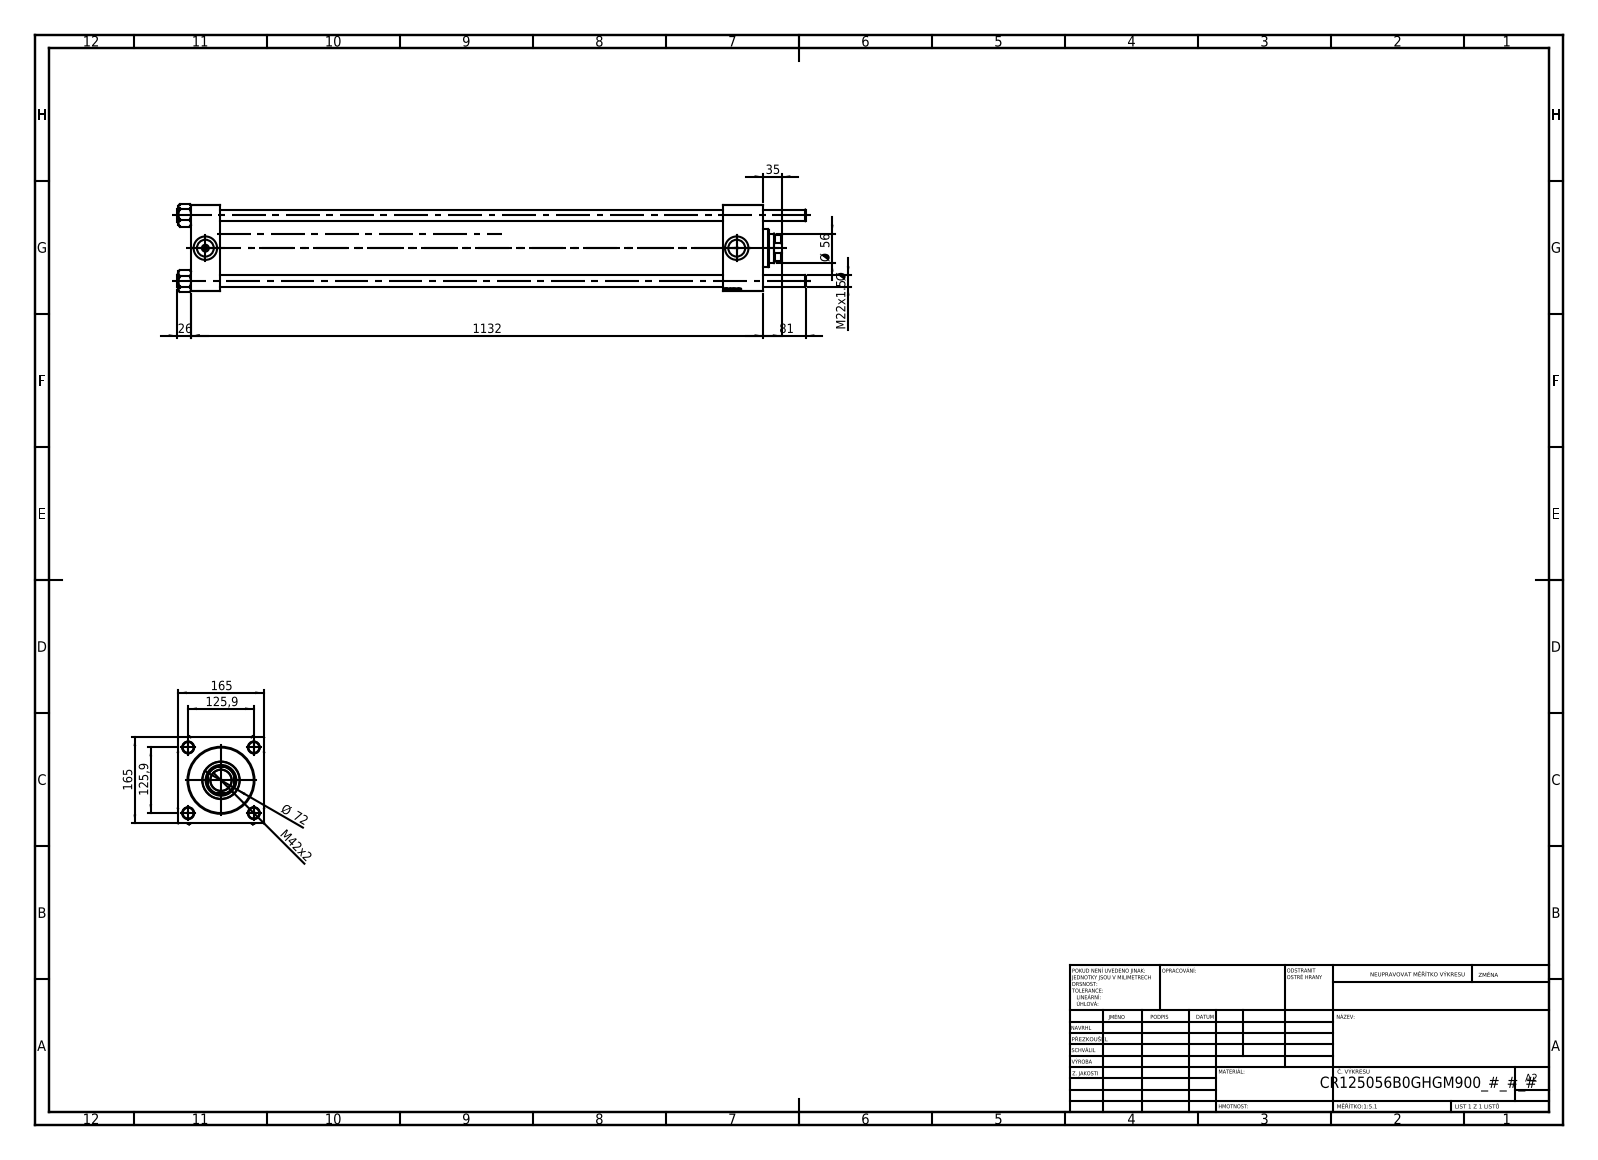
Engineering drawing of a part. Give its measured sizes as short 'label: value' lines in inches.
name: V215_VC_A; V215CR_VCP_B; V215CR_B-1; NUT_M5_B (+1 more)
written by: SolidWorks 2019 (CONFIG_CONTROL_DESIGN)
unit: in
bodies: 11 solids, 1206 faces (480 planar, 78 cylindrical, 648 other)
size: 47.402 × 6.653 × 6.499
volume: 564.3 in³; area: 2 564 in²
holes: 4× ⌀0.866, 2× ⌀0.276, 2× ⌀1.269, 2× ⌀1.772, 1× ⌀1.594, 1× ⌀2.205, 1× ⌀2.323, 1× ⌀3.78, 1× ⌀4.921, 1× ⌀4.941
bosses: 4× ⌀0.984, 1× ⌀5.157, 1× ⌀2.835
rounds: 1× R1.063
face distances: 6.496, 2.165, 43.189, 41.024, 40.118, 37.953, 3.071, 42.059, 39.894, 1.941
hole spacings: 3.505, 4.957, 7.01, 40.098
